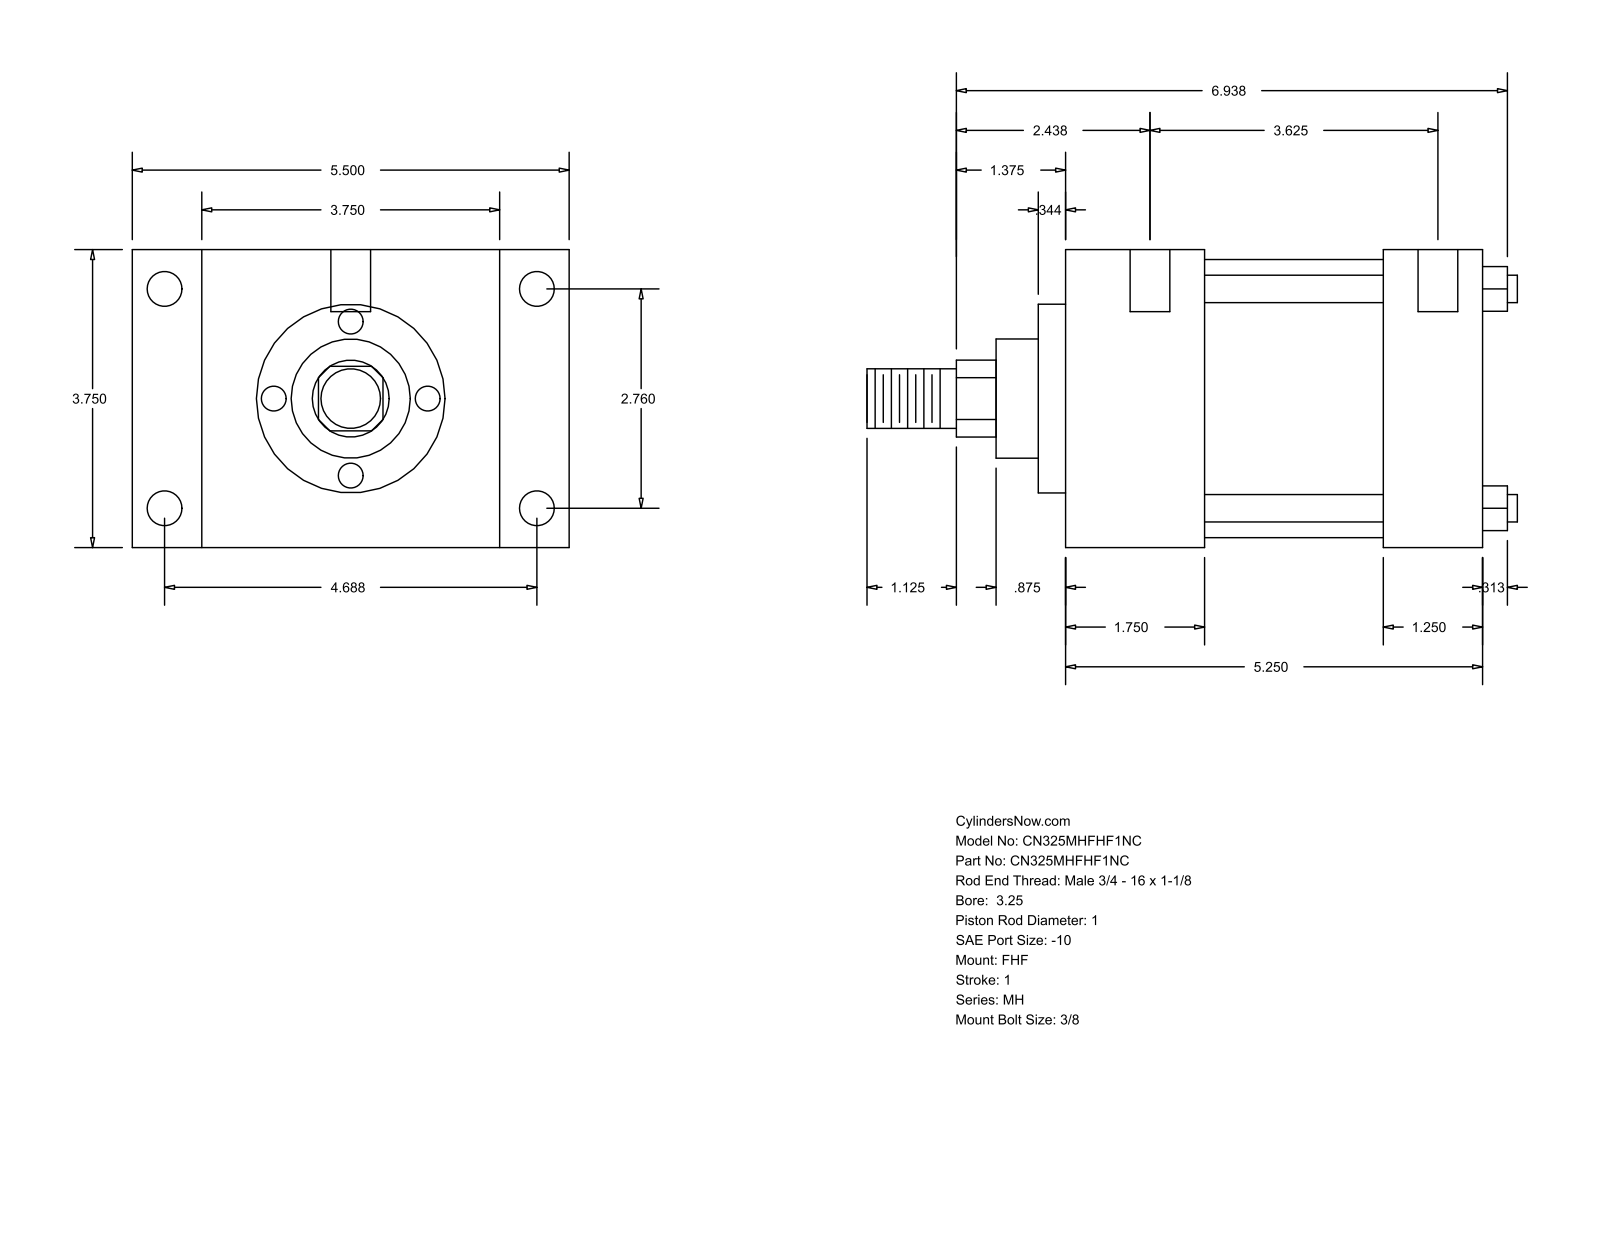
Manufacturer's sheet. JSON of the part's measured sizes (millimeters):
{"part_name": "MH_FHF__0325_1", "step_written_by": "GSSL Pune (CONFIG_CONTROL_DESIGN)", "units": "millimeters", "bodies": {"solids": 0, "faces": 90, "planar": 61, "cylindrical": 29, "other": 0}, "overall_size": [207.96, 139.7, 95.25], "round_holes": [[5.56, 4], [11.13, 4], [12.7, 2]], "round_bosses_or_shafts": [[8.76, 4], [88.9, 1], [60.33, 1], [38.1, 1], [25.4, 1], [19.05, 1]], "partial_cylinders_radius": [[12.29, 1]], "face_to_face_distances": [95.24, 133.36, 44.46, 88.9, 22.23, 117.47, 139.7, 101.61, 57.15, 31.75], "hole_center_spacings": [70.1, 98.42, 119.06, 138.16, 1.58, 4.76, 92.08, 93.66]}
